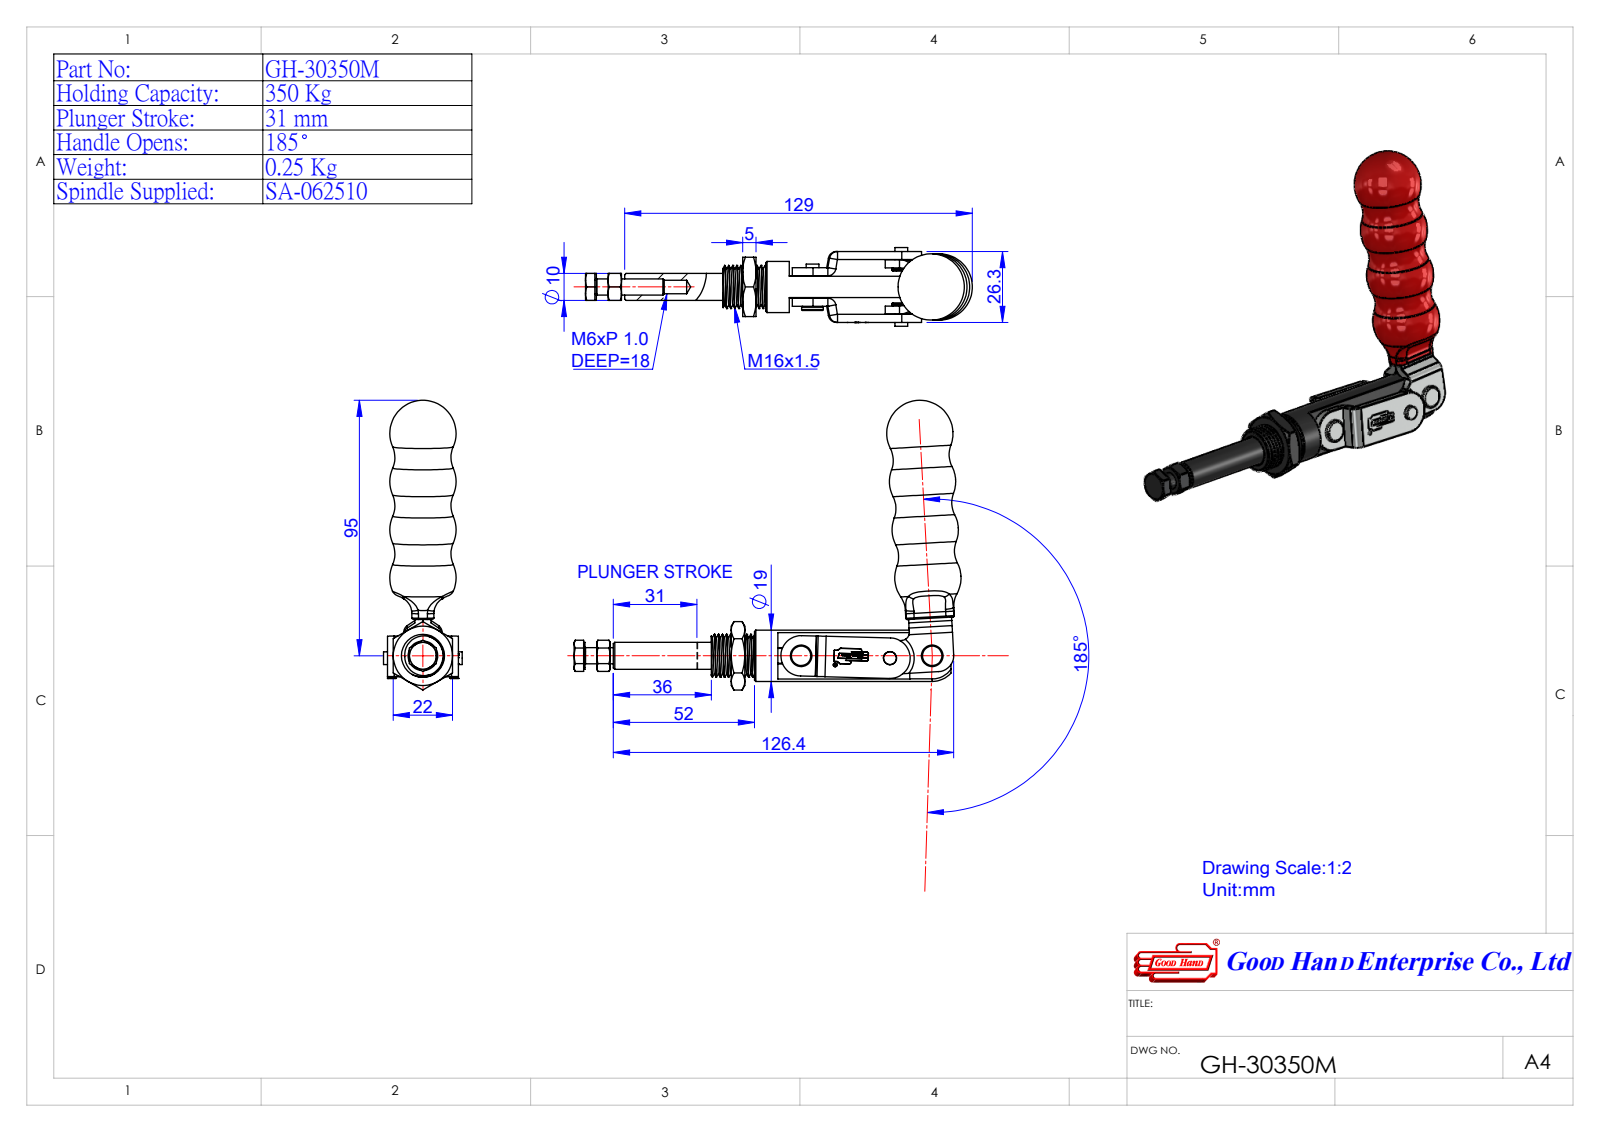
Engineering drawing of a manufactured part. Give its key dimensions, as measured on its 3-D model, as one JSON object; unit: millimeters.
{"part_name": "430350M32-1^GH-30350M(簡化); Group1^GH-30350M(簡化); Group5^GH-30350M(簡化); Group3^GH-30350M(簡化) (+2 more)", "step_written_by": "SolidWorks 2016 (AUTOMOTIVE_DESIGN)", "units": "millimeters", "bodies": {"solids": 5, "faces": 783, "planar": 337, "cylindrical": 127, "other": 319}, "overall_size": [143.62, 107.52, 29.2], "volume_mm3": 54314, "surface_area_mm2": 24407, "round_holes": [[3.5, 3], [4.9, 2], [1.38, 1], [5, 1], [10, 1], [15.8, 1]], "round_bosses_or_shafts": [[4.73, 3], [8, 2], [19, 1], [16, 1], [7, 1], [6, 1], [1.32, 1]], "partial_cylinders_radius": [[3, 9], [0.53, 3], [0.56, 3], [0.5, 2], [6, 2], [6.36, 2], [7.5, 2], [0.59, 1]], "face_to_face_distances": [3, 17.25, 6.05, 14.25, 6, 3.05, 9.2, 17.1, 23.3, 6.2], "hole_center_spacings": [13.05, 15.7, 20.52, 32.99, 36.21, 48.66]}
